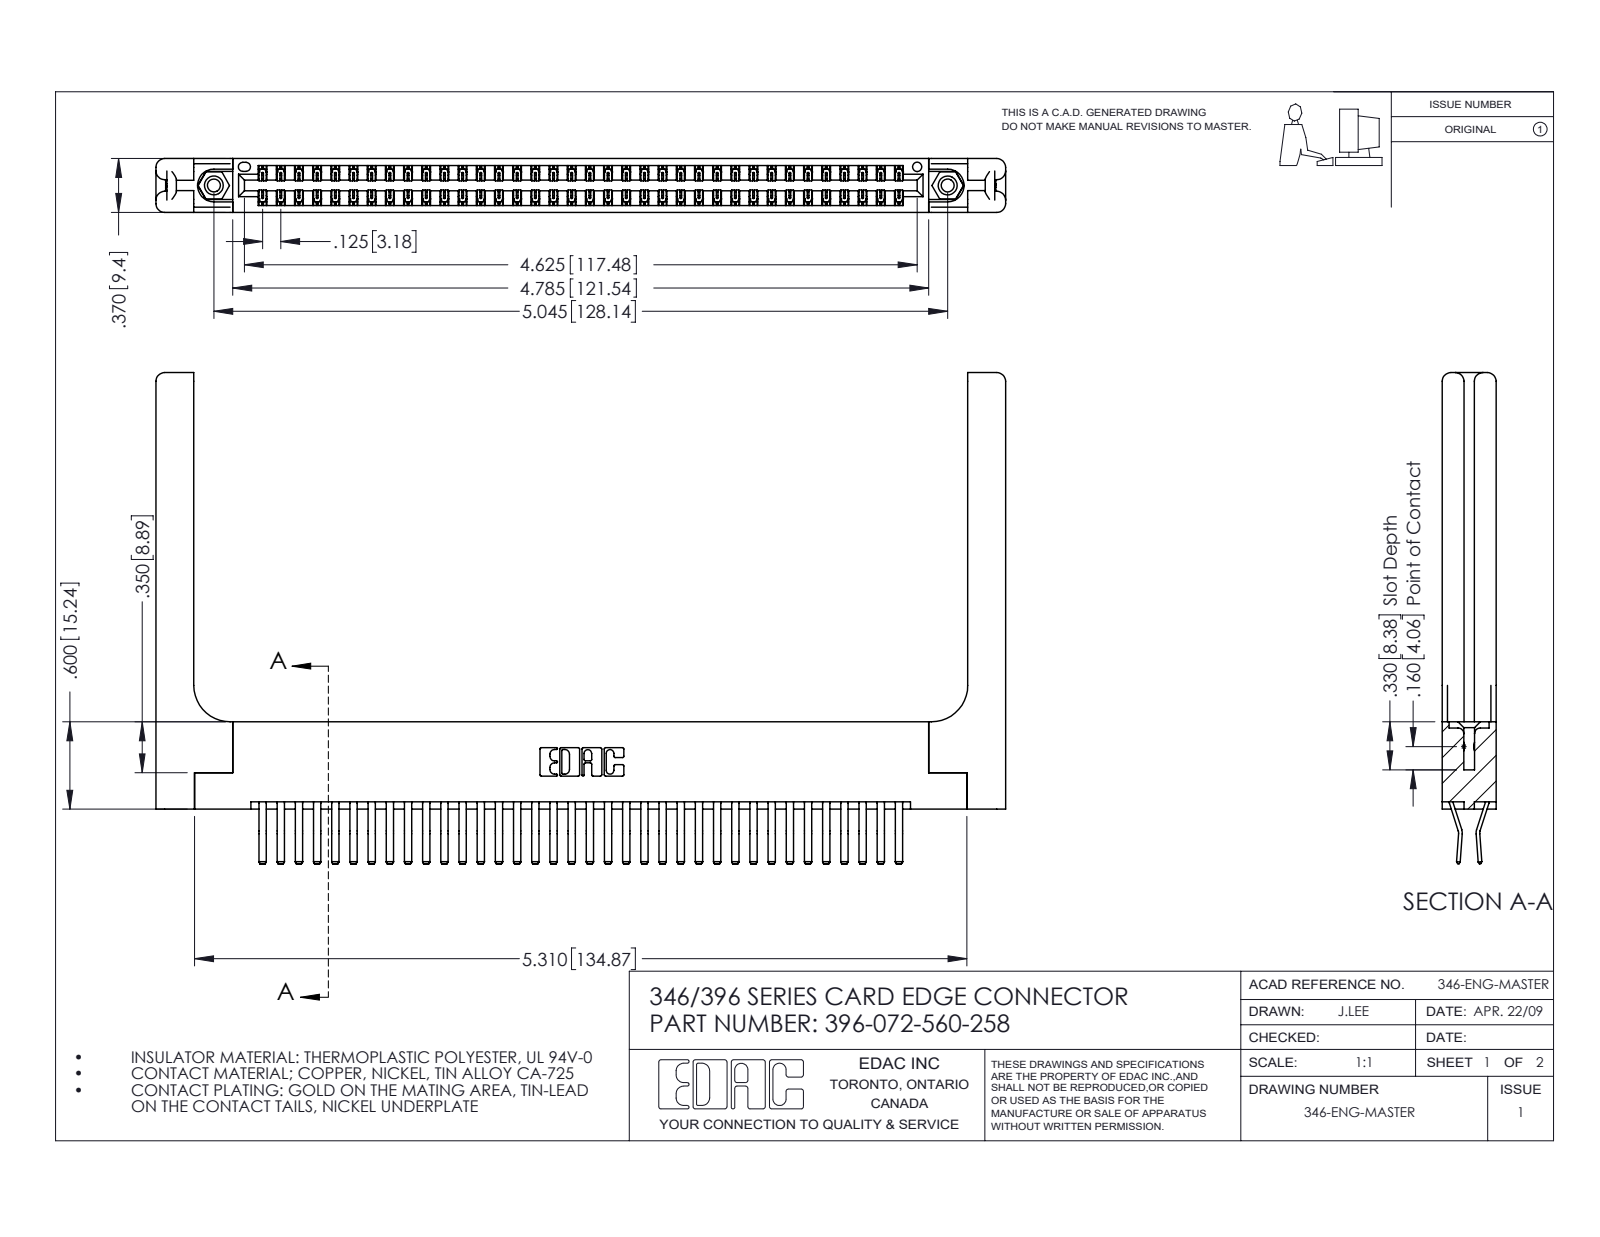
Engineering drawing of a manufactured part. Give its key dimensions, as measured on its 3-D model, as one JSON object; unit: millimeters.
{"part_name": "345-250-001_345-250-001-102; 396-072-560-258; 345-292-001_560 Tail; 346-220-058_345-220-058 (+1 more)", "step_written_by": "SolidWorks 2016 (CONFIG_CONTROL_DESIGN)", "units": "millimeters", "bodies": {"solids": 77, "faces": 4266, "planar": 2744, "cylindrical": 1462, "other": 60}, "overall_size": [148.4, 85.7, 9.4], "volume_mm3": 22380, "surface_area_mm2": 26610, "round_holes": [[2.3, 2], [3.2, 2], [4, 2], [1.6, 1]], "round_bosses_or_shafts": [[3.9, 2]], "partial_cylinders_radius": [[0.2, 108], [0.3, 22], [1.5, 16], [0.2, 6], [0.8, 6], [0.7, 3], [0.3, 2], [0.4, 2]], "face_to_face_distances": [9.4, 1.2, 8.2, 1.8, 3.8, 3.8, 0.6, 6.4, 7.6, 7], "hole_center_spacings": [6.2, 122.8, 128.1]}
